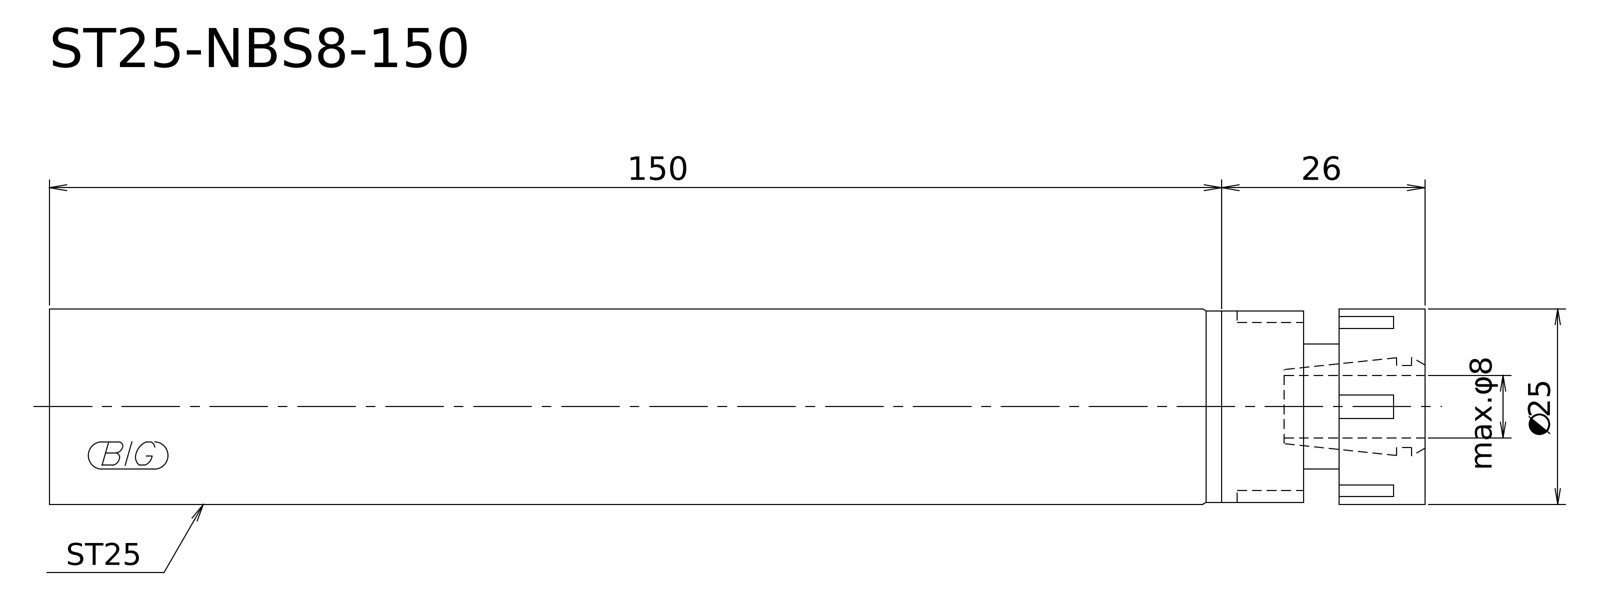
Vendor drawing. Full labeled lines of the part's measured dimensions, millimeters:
STEP written by: Kubotek KeyCreator V8.5.1 (14335) (CONFIG_CONTROL_DESIGN)
Units: millimetres
Bodies: 1 solid, 9 faces (4 planar, 4 cylindrical, 1 other)
Overall size (bounding box): 176 × 25 × 25
Volume: 84 836 mm³ · Surface area: 15 222 mm²
Round bosses / shafts (diameter × count): ⌀25 ×1, ⌀24.5 ×1, ⌀16 ×1
Main face-to-face distances: 176, 11, 165, 15.5, 4.5, 160.5
